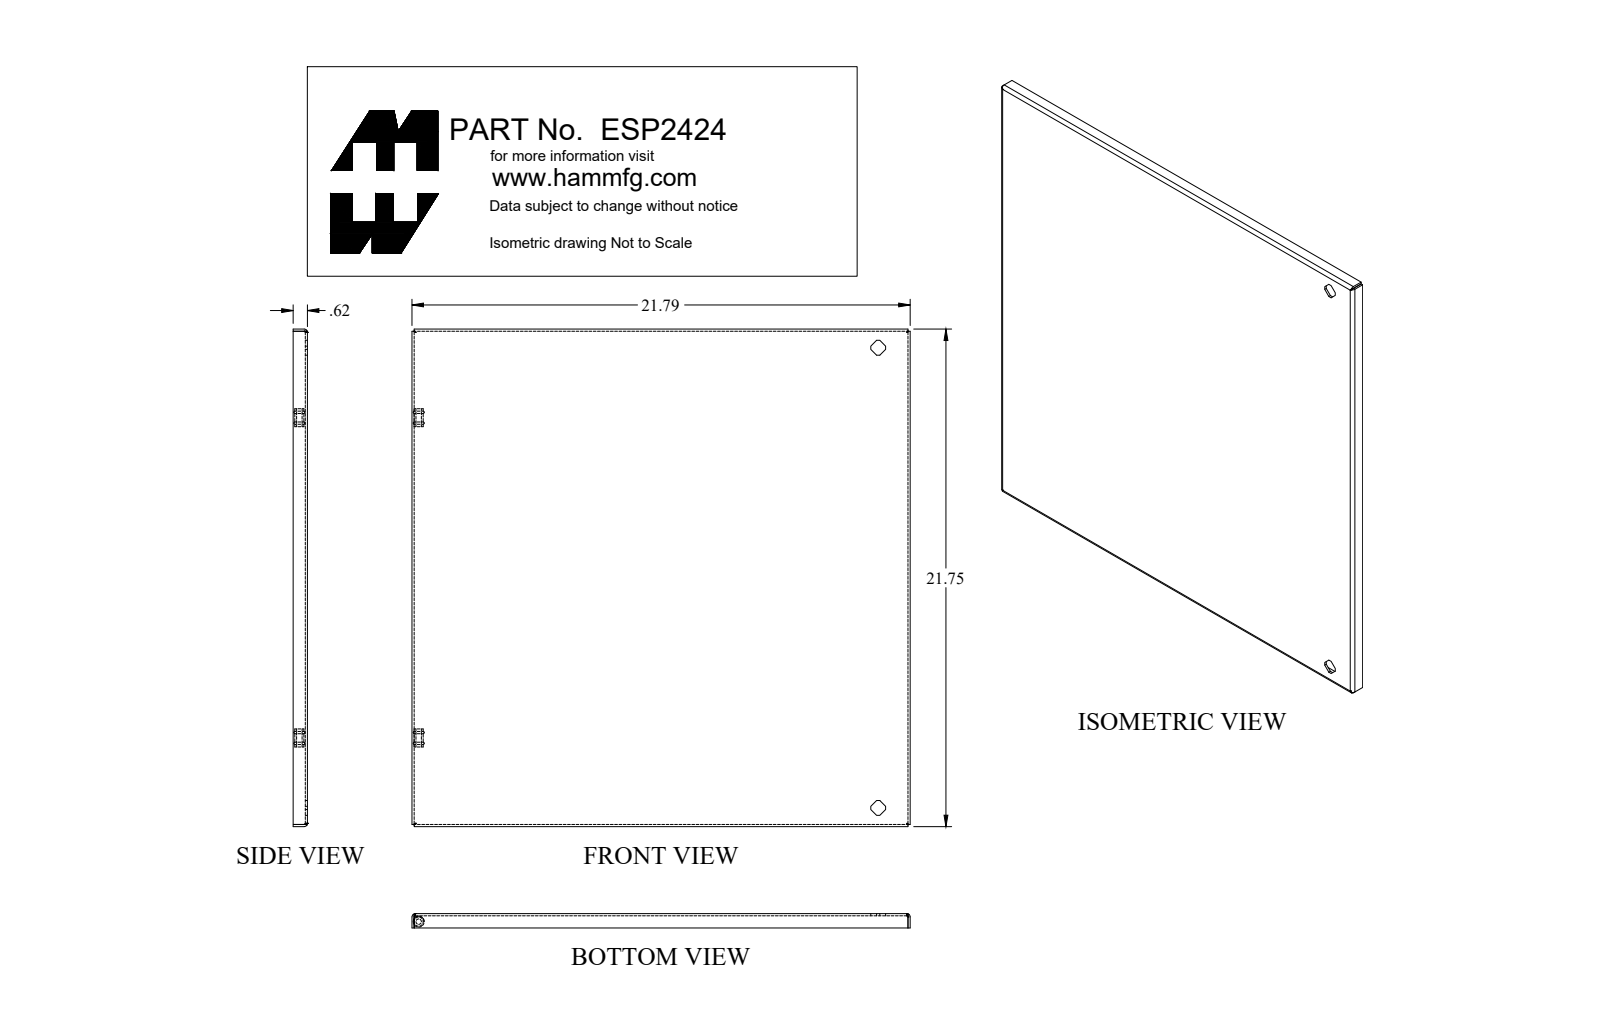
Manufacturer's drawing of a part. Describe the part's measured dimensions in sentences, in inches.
The part is named "ESP2424". Its 3-D file was written by "SolidWorks 2018 (AUTOMOTIVE_DESIGN)". It is 13 solids with 584 faces: 354 planar, 174 cylindrical and 56 other. Overall it measures 23.706 by 21.75 by 9.953 inches. Its volume is 64.02 cubic inches and its surface area 1 563 square inches. Round holes: 2 of diameter 0.136, 2 of diameter 0.242, 2 of diameter 0.516. Round bosses or shafts: 6 of diameter 0.232, 2 of diameter 0.788, 2 of diameter 0.496, 2 of diameter 0.435, 2 of diameter 0.356, 1 of diameter 0.535, 1 of diameter 0.535. Partial cylindrical surfaces (rounded edges, fillets, slot ends): 28 of radius 0.048, 24 of radius 0.01, 6 of radius 0.036, 6 of radius 0.108, 4 of radius 0.06, 4 of radius 0.143, 4 of radius 0.153, 4 of radius 0.156. The main face-to-face distances are 0.095, 0.072, 22.008, 0.038, 0.775, 0.813, 22.08, 0.775, 20.062, 0.78. The hole center spacings are 14, 20.159.
